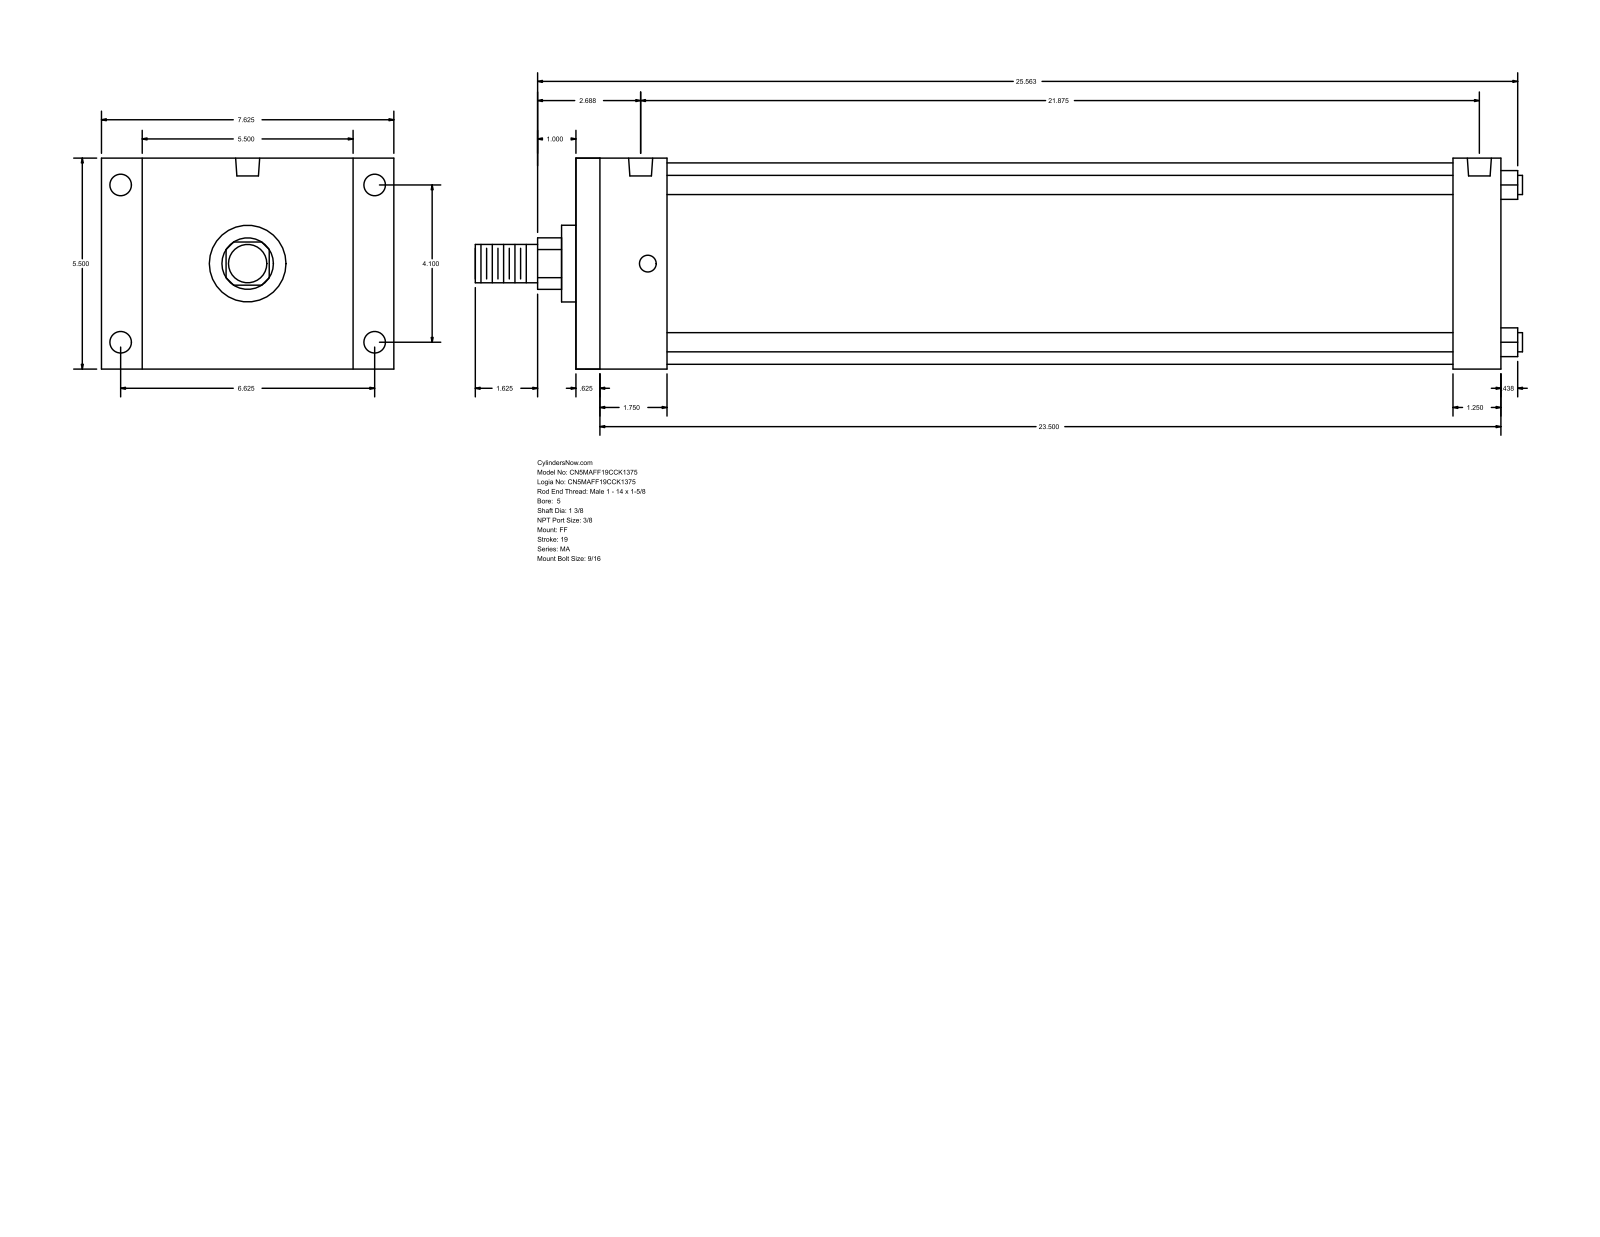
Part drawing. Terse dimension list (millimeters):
name: MA_FF__0500_1.375
written by: GSSL Pune (CONFIG_CONTROL_DESIGN)
unit: mm
bodies: 0 solids, 92 faces (64 planar, 28 cylindrical, 0 other)
size: 693.74 × 193.68 × 139.7
holes: 4× ⌀11.11, 4× ⌀14.29, 2× ⌀15.93
bosses: 4× ⌀12.7, 1× ⌀133.35, 1× ⌀50.8, 1× ⌀34.92, 1× ⌀25.4
rounds: 1× R17.06
face distances: 139.7, 612.77, 15.87, 596.9, 581.02, 565.15, 31.75, 60.32, 44.45, 520.7
hole spacings: 4.77, 104.14, 168.28, 197.9, 546.09, 550.86, 555.63
